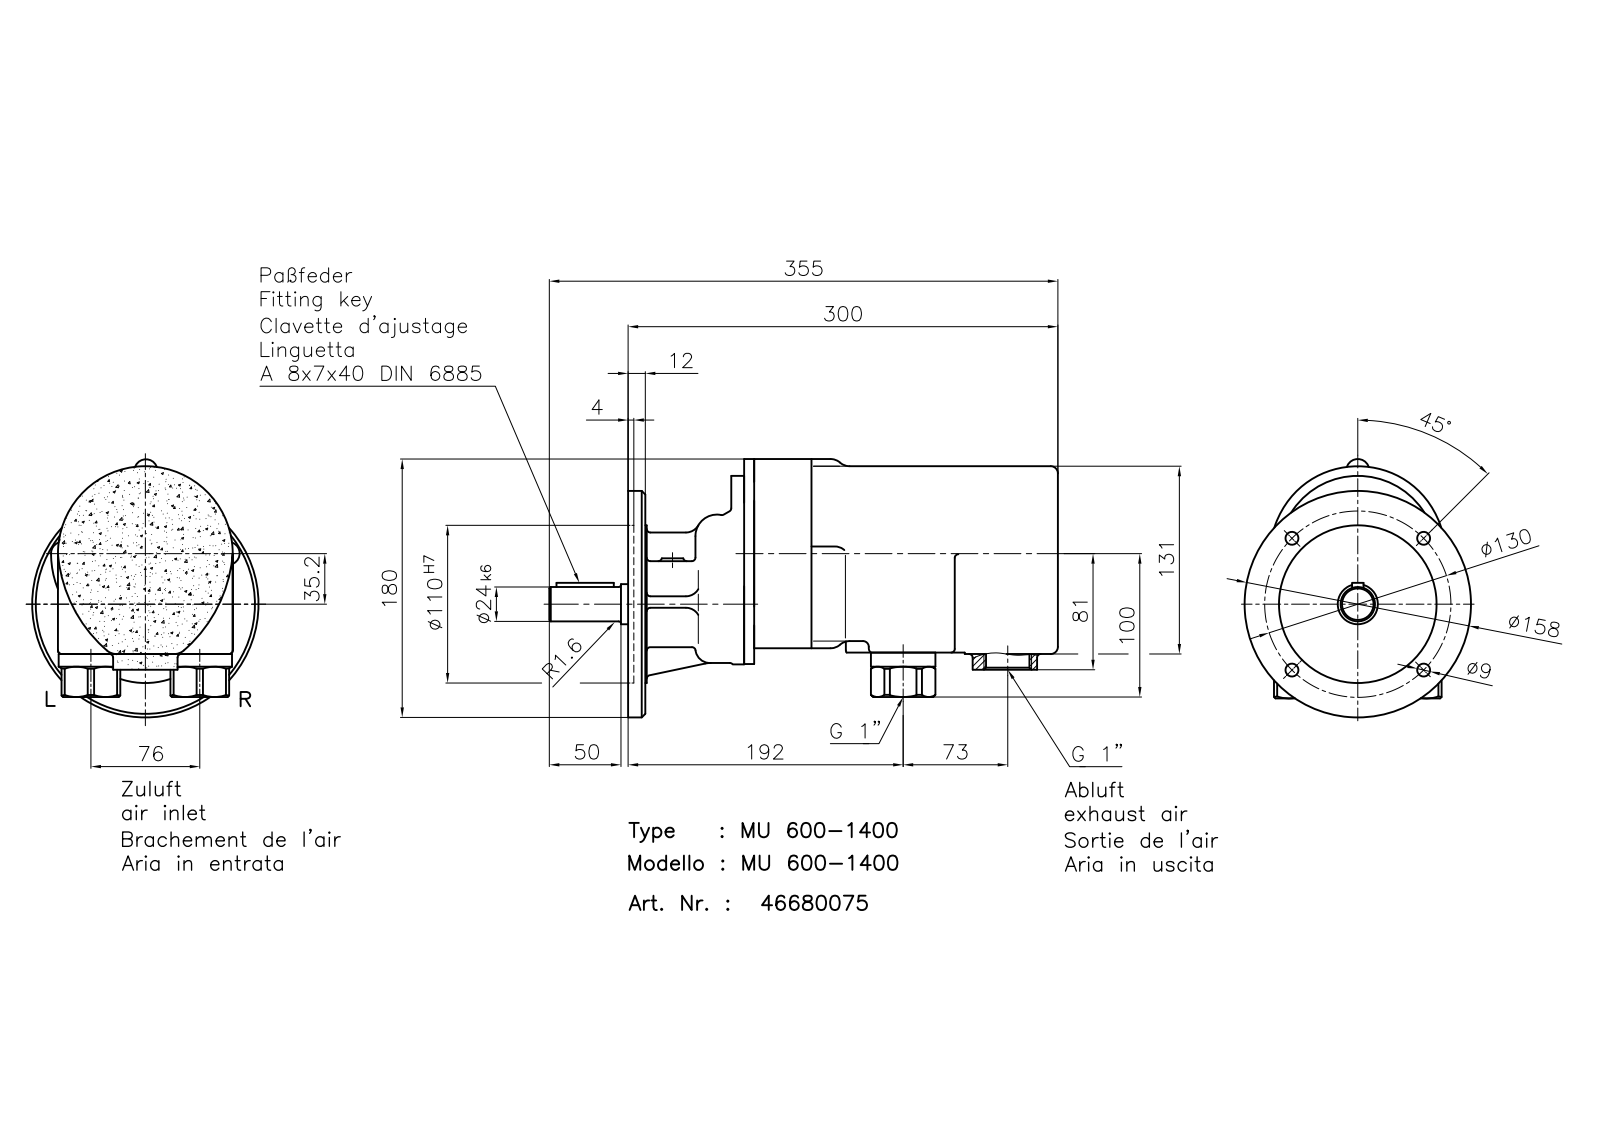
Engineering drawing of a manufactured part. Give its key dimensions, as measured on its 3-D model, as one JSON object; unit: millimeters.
{"part_name": "MU 600-1400_46680075", "step_written_by": "Autodesk Inventor 2008 (AUTOMOTIVE_DESIGN)", "units": "millimeters", "bodies": {"solids": 1, "faces": 643, "planar": 227, "cylindrical": 212, "other": 204}, "overall_size": [355, 180.25, 158], "volume_mm3": 3435000, "surface_area_mm2": 240501, "round_holes": [[18, 2], [33.25, 2], [6.4, 1], [7, 1], [80, 1], [110, 1]], "round_bosses_or_shafts": [[11, 5], [10, 5], [6, 5], [41, 2], [24.4, 2], [158, 1], [122, 1], [82, 1]], "partial_cylinders_radius": [[2.5, 27], [2, 25], [4, 14], [5, 11], [8, 10], [10, 6], [6, 5], [1.6, 4]], "face_to_face_distances": [300, 12, 68, 4, 288, 8, 9, 81, 69, 219], "hole_center_spacings": [76]}
